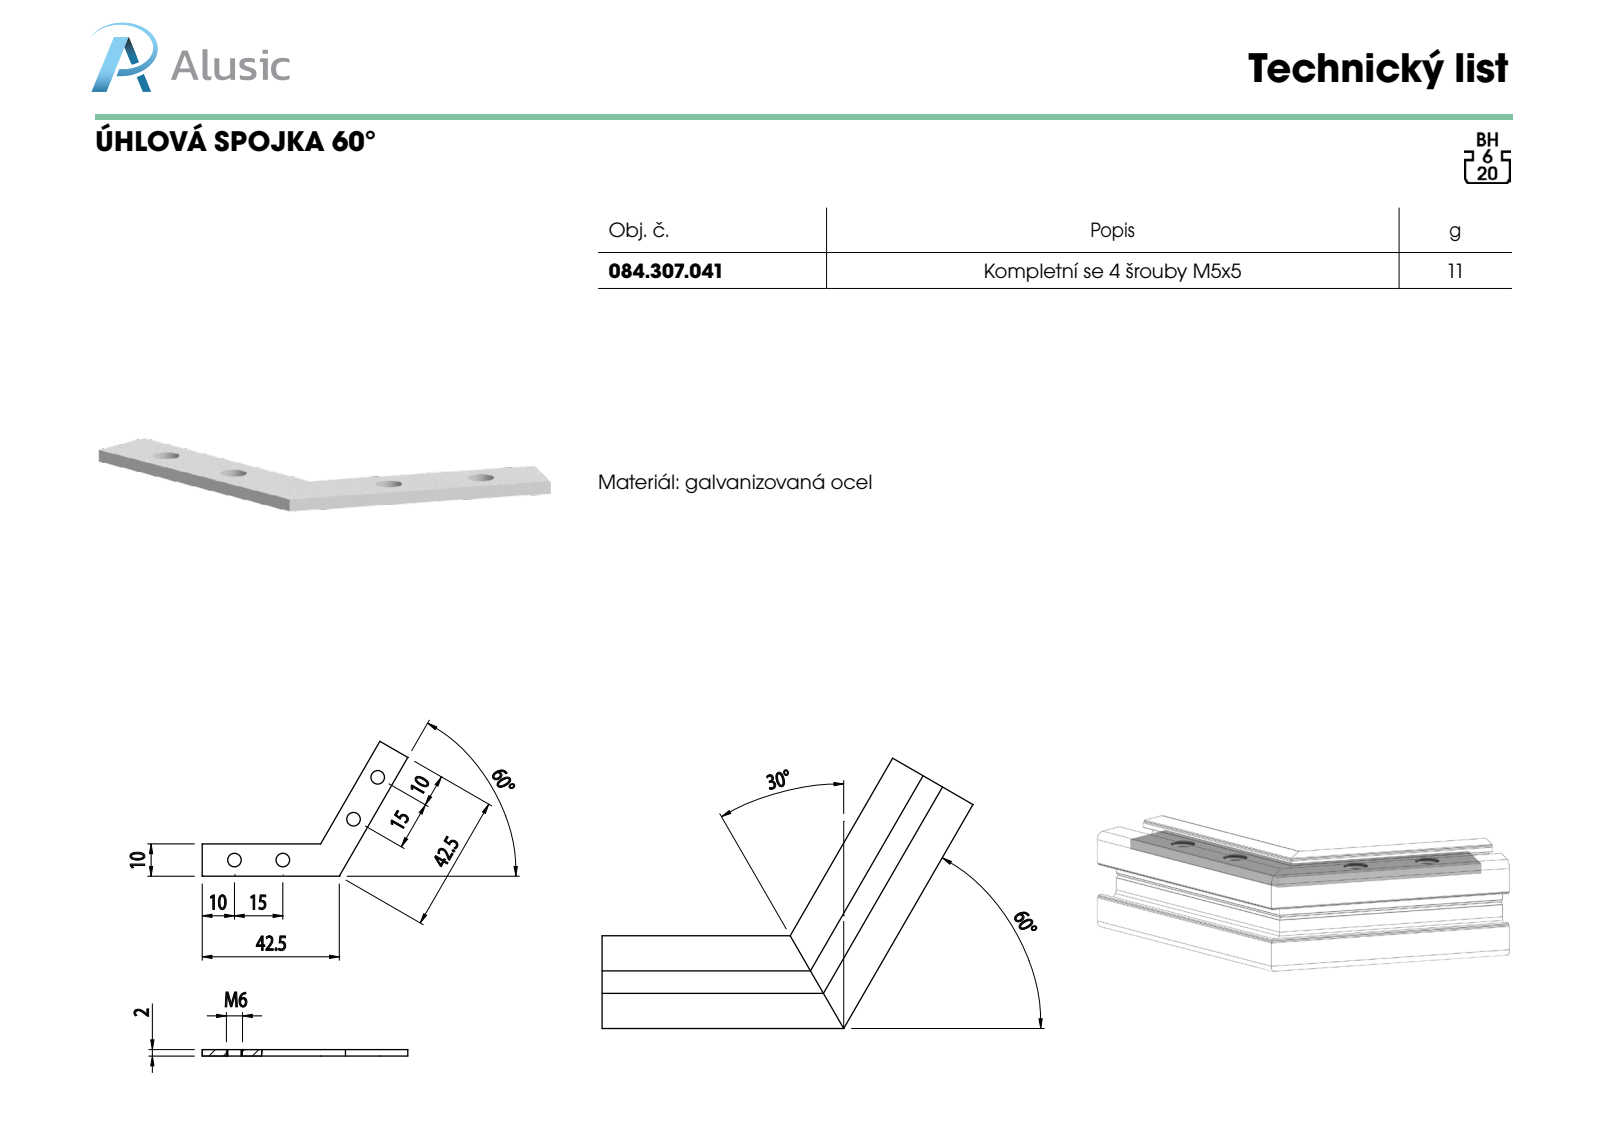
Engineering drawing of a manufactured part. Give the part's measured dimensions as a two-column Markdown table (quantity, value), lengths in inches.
| quantity | value |
| --- | --- |
| part name | 084.307.041 |
| STEP written by | SolidWorks 2012 (CONFIG_CONTROL_DESIGN) |
| units | inches |
| bodies | 1 solid, 16 faces (8 planar, 8 cylindrical, 0 other) |
| overall size | 2.51 × 1.646 × 0.079 |
| volume | 0.087 in³ |
| surface area | 2.961 in² |
| round holes (diameter × count) | 0.197 × 4 |
| main face-to-face distances | 0.079, 0.394 |
| hole center spacings | 0.591, 1.537, 0.996, 2.019 |
